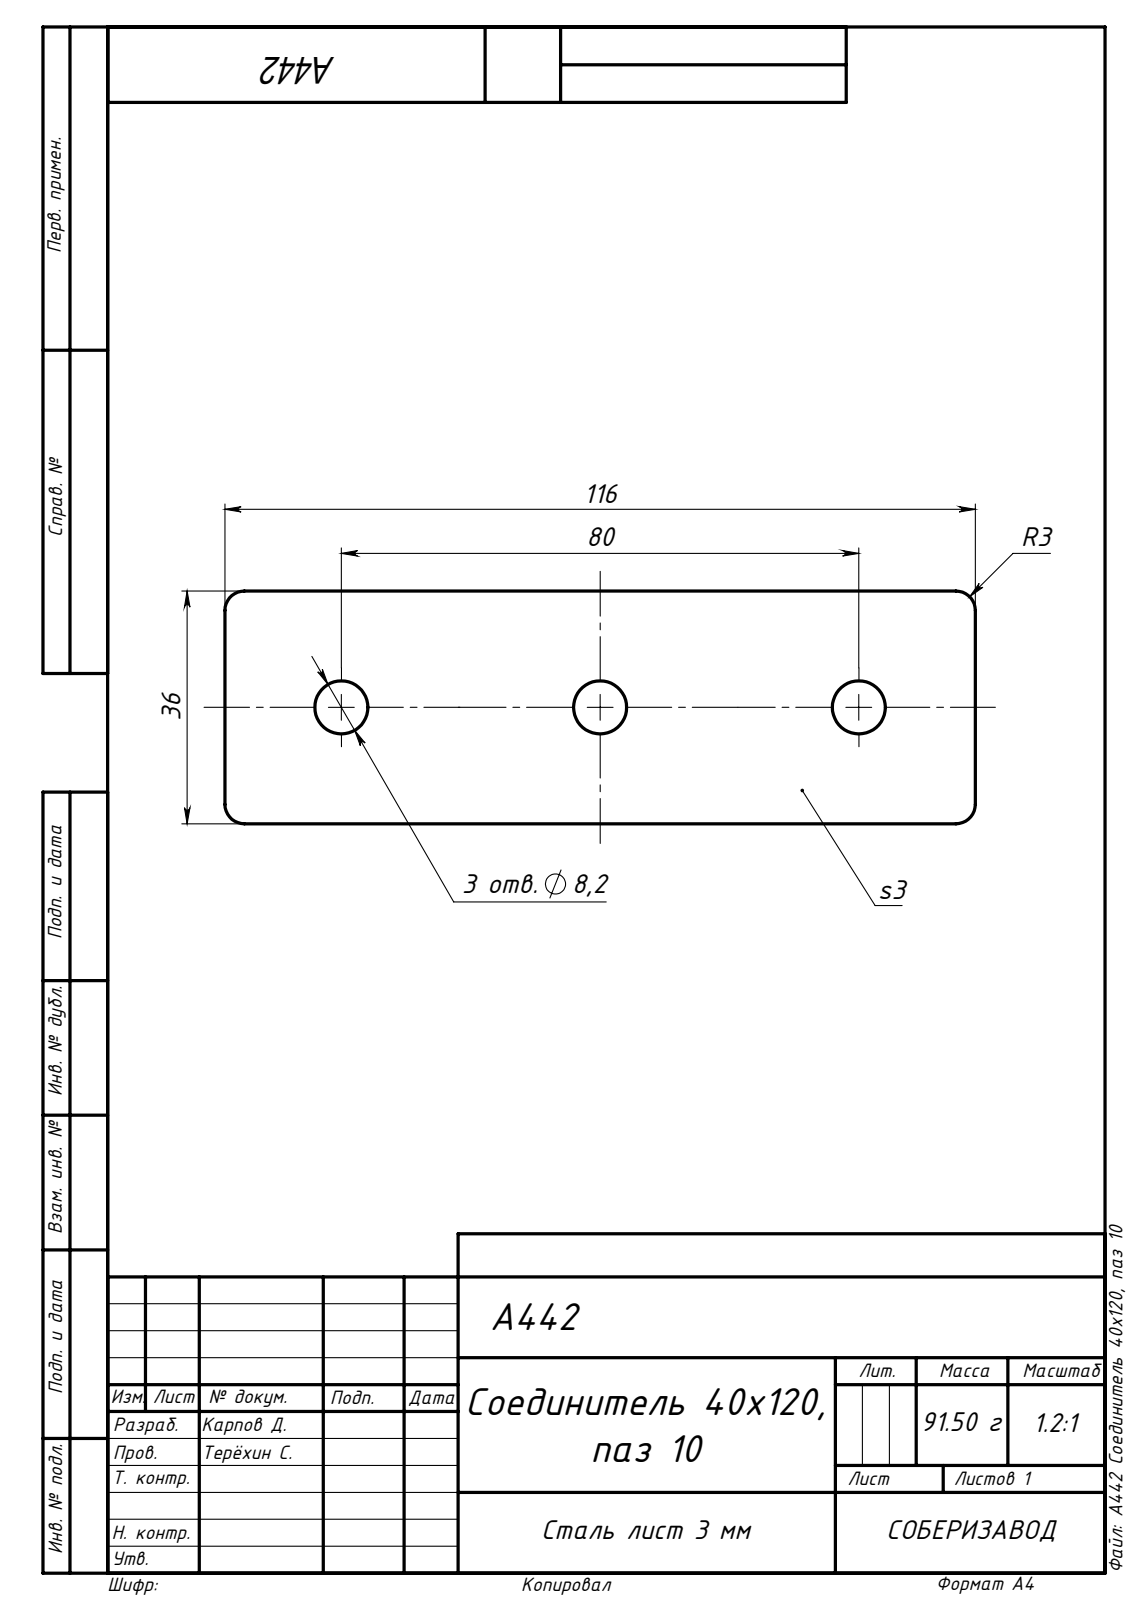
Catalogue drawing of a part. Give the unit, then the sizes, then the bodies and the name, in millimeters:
Units: millimetres
Overall size (bounding box): 116 × 36 × 3
Round holes (diameter × count): ⌀8.2 ×3
Partial cylindrical surfaces — rounded edges, fillets, slot ends (radius × count): R3 ×4
Main face-to-face distances: 3, 36, 116
Hole centre spacings: 40, 80
Volume: 12 030 mm³ · Surface area: 9 148 mm²
Bodies: 1 solid, 16 faces (6 planar, 10 cylindrical, 0 other)
STEP written by: SolidWorks 2020 (AUTOMOTIVE_DESIGN)
